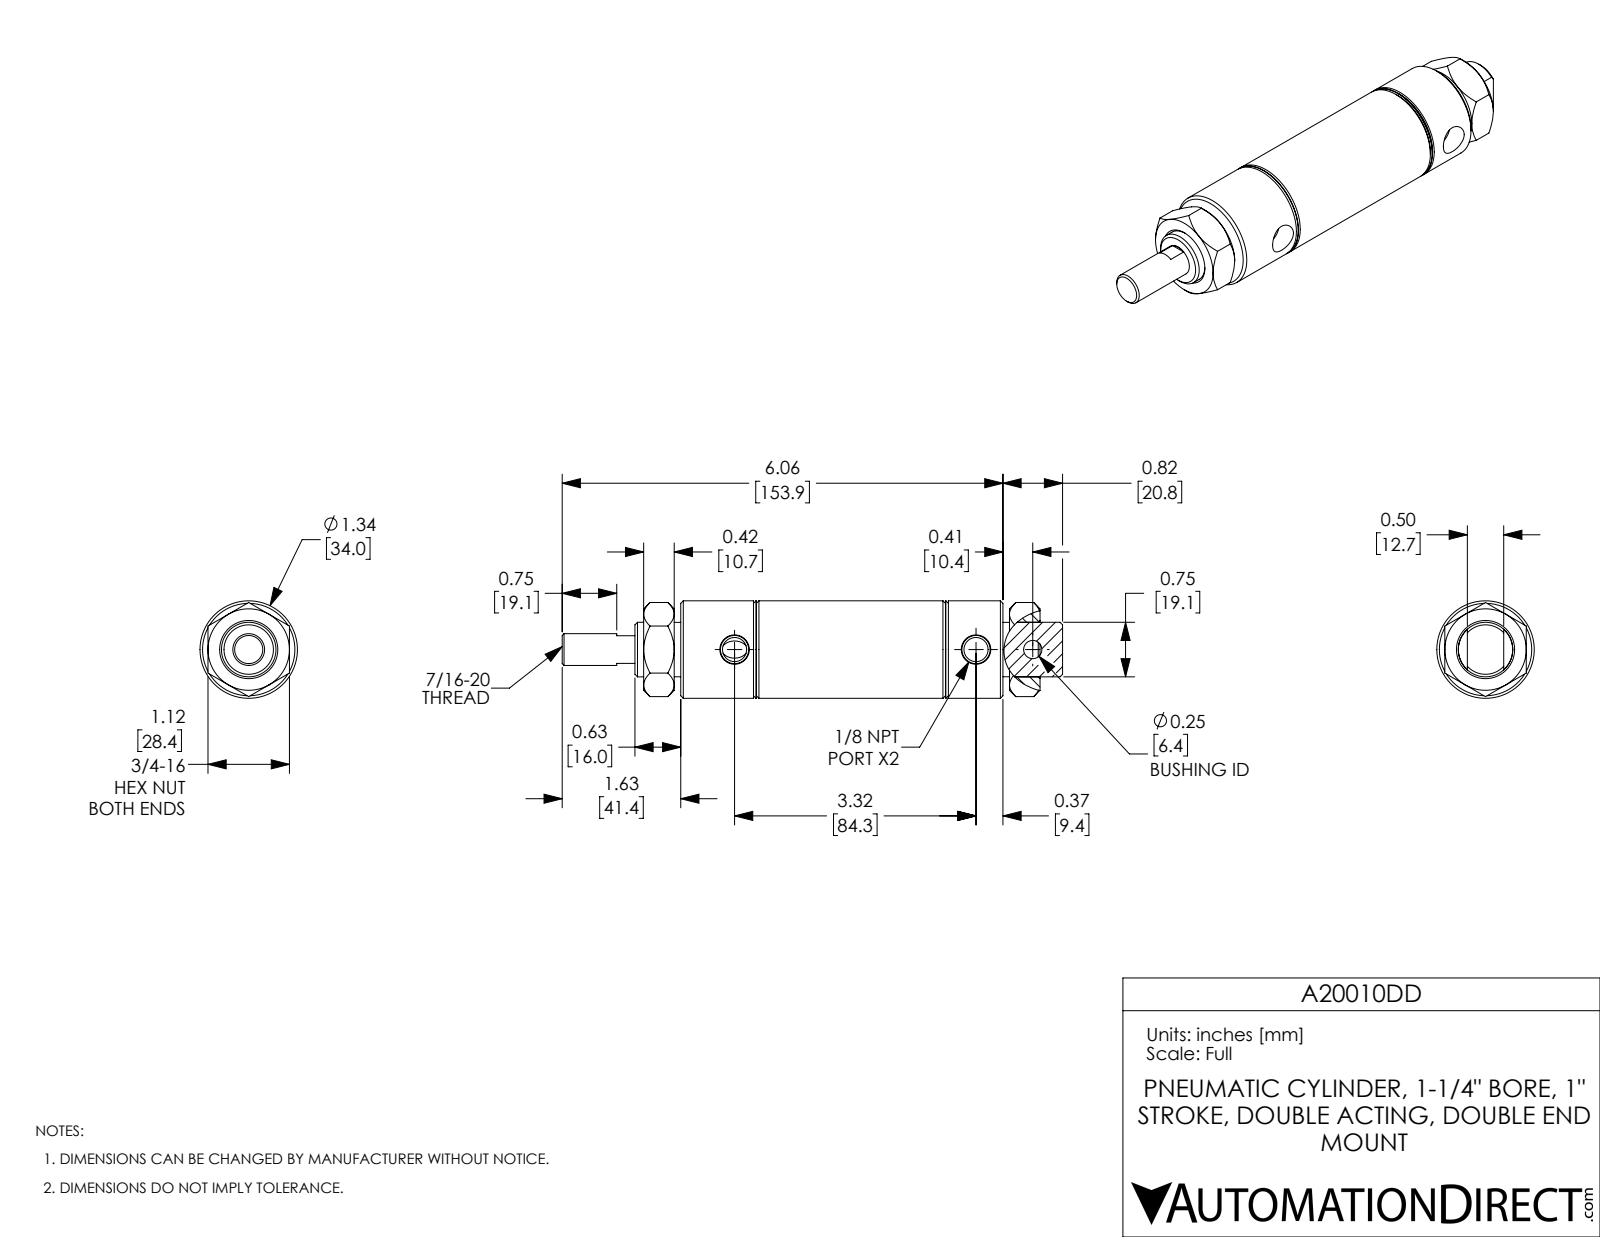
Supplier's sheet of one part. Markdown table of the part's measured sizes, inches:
| quantity | value |
| --- | --- |
| part name | A20010DD; A20010DD_Mounting Nut_D-3556; A20010DD-Rod; A20010DD-MainBody |
| STEP written by | SolidWorks 2017 (AUTOMOTIVE_DESIGN) |
| units | inches |
| bodies | 4 solids, 138 faces (44 planar, 36 cylindrical, 58 other) |
| overall size | 6.88 × 1.34 × 1.34 |
| volume | 6.272 in³ |
| surface area | 54.86 in² |
| round holes (diameter × count) | 0.332 × 2, 0.251 × 1, 0.437 × 1, 0.75 × 1, 1.25 × 1 |
| round bosses / shafts (diameter × count) | 1.34 × 1, 0.747 × 1 |
| main face-to-face distances | 1.465, 2.965, 0.5, 1.12, 1, 1.5, 0.31, 1.965, 0.42, 5.03 |
| hole center spacings | 0.78, 3.32, 4.1 |
